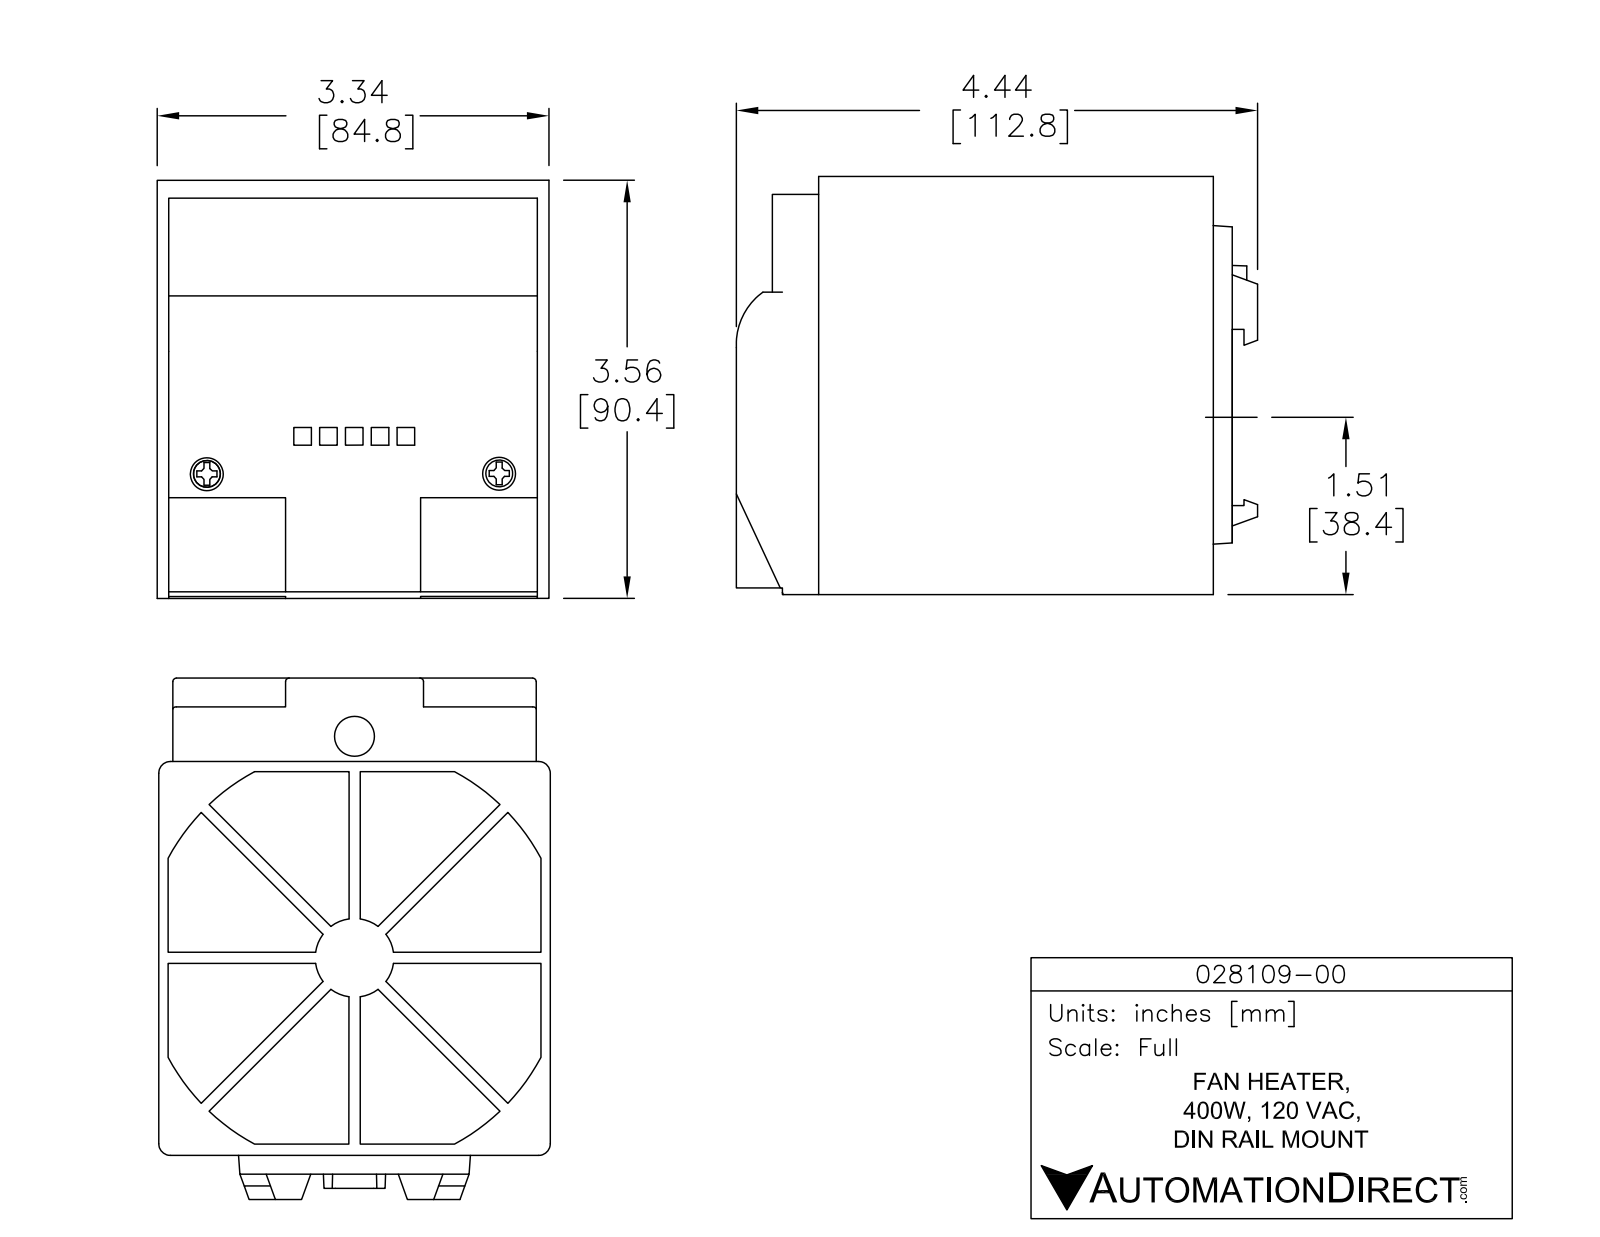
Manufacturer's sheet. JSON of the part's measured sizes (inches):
{"part_name": "028109-00", "step_written_by": "SolidWorks 2013 (AUTOMOTIVE_DESIGN)", "units": "inches", "bodies": {"solids": 1, "faces": 408, "planar": 219, "cylindrical": 153, "other": 36}, "overall_size": [4.44, 3.56, 3.335], "volume_in3": 45.38, "surface_area_in2": 92.95, "round_holes": [[0.275, 2], [0.34, 1]], "round_bosses_or_shafts": [[0.22, 2]], "partial_cylinders_radius": [[0.065, 60], [0.03, 23], [0.07, 4], [0.1, 4], [0.25, 1], [0.335, 1], [1.8, 1]], "face_to_face_distances": [3.335, 0.1, 3.455, 4.065, 3.355, 0.12, 3.215, 4.225, 0.16, 3.555], "hole_center_spacings": [2.43]}
